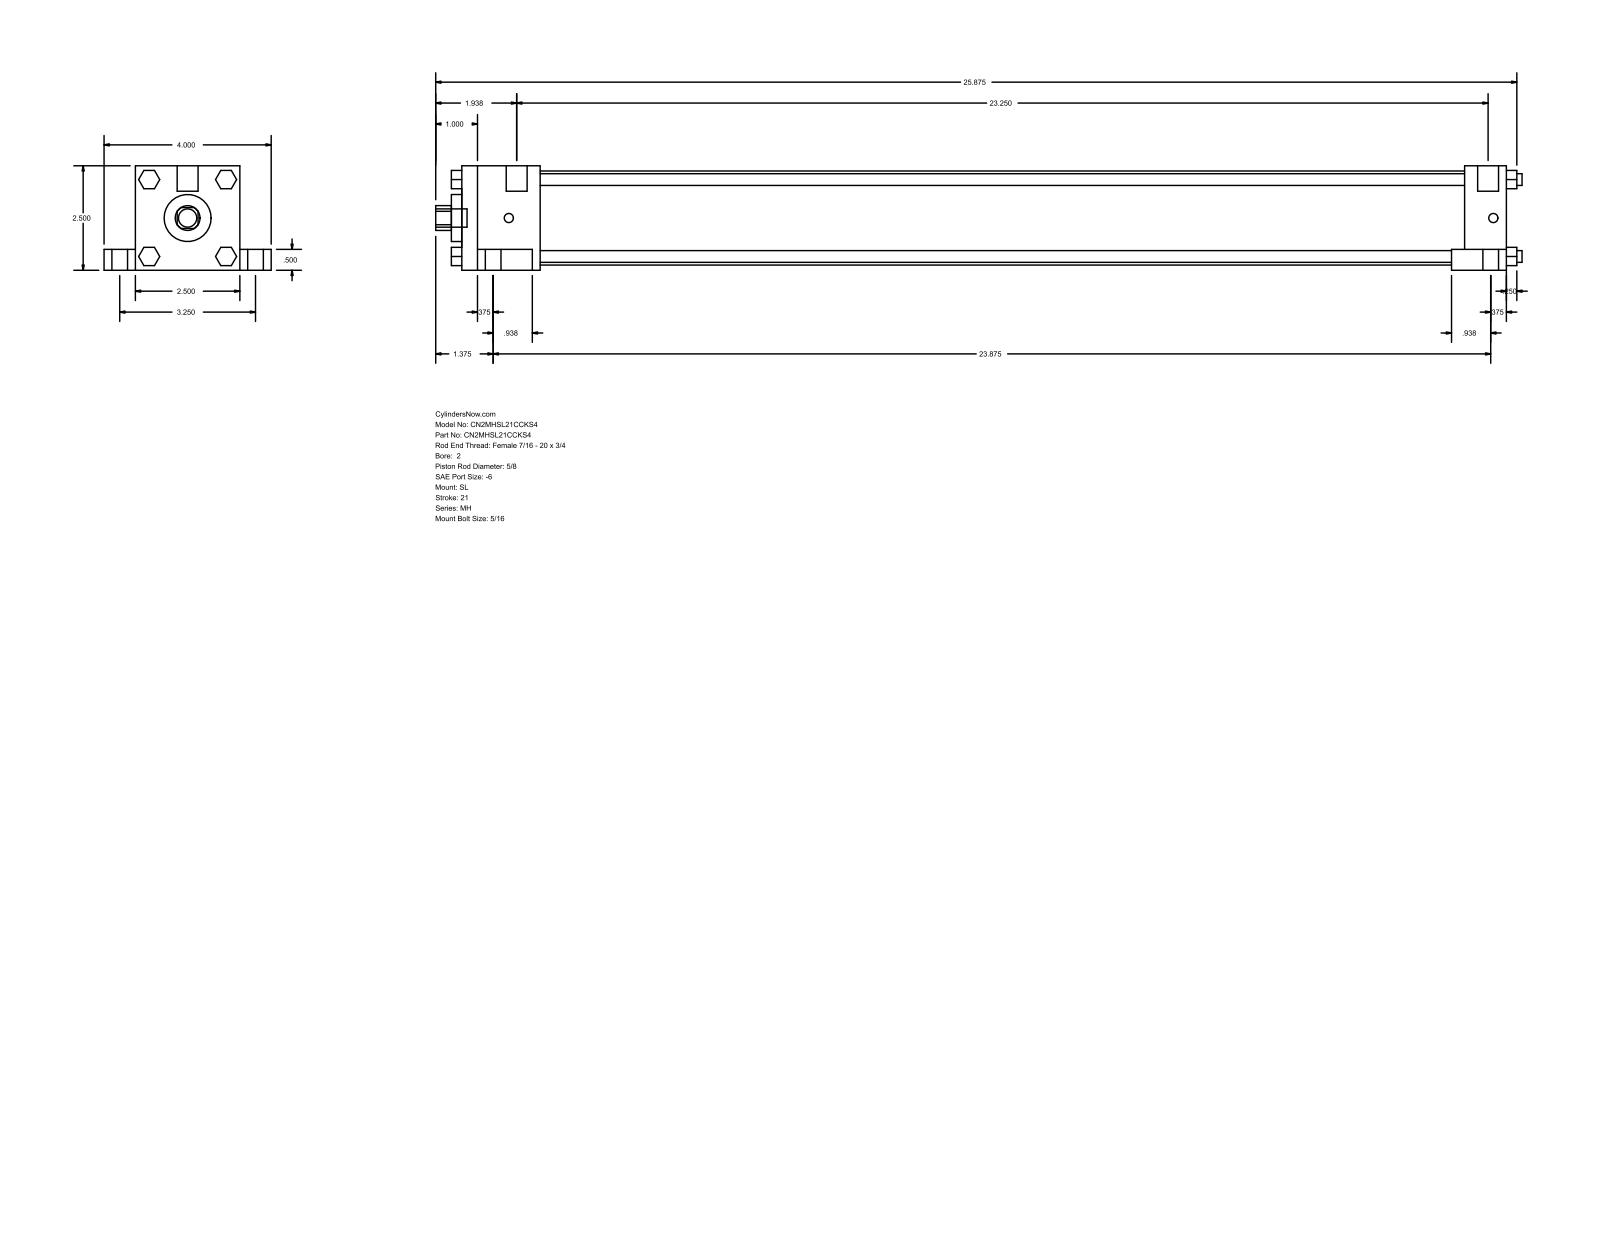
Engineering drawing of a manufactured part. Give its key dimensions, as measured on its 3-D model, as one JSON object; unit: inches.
{"part_name": "MH_SL__0200_0.625", "step_written_by": "GSSL Pune (CONFIG_CONTROL_DESIGN)", "units": "inches", "bodies": {"solids": 0, "faces": 148, "planar": 112, "cylindrical": 36, "other": 0}, "overall_size": [26, 4, 2.5], "round_holes": [[0.625, 1], [1.125, 1], [2.25, 1]], "round_bosses_or_shafts": [[0.625, 4], [0.375, 4], [0.281, 4], [0.219, 4], [0.5, 2], [0.437, 1]], "partial_cylinders_radius": [[0.297, 1]], "face_to_face_distances": [2.5, 25, 0.5, 0.75, 2, 3.25, 1, 24, 1.875, 22.125]}
